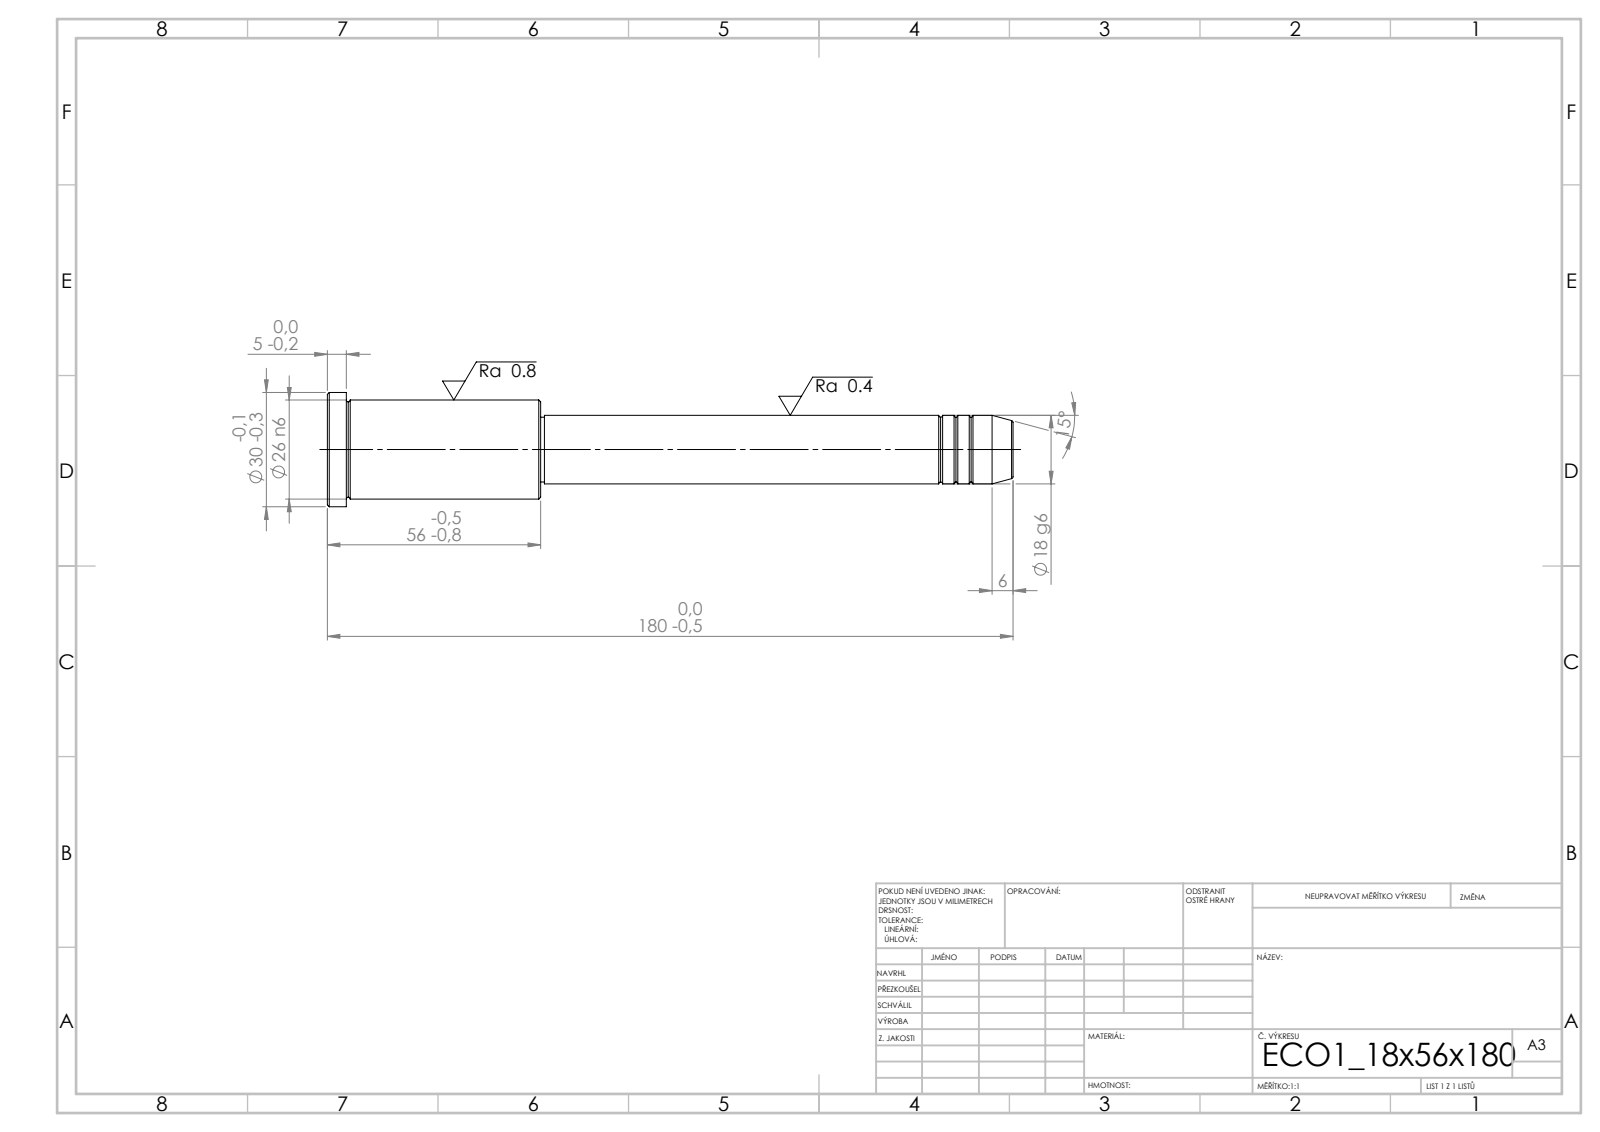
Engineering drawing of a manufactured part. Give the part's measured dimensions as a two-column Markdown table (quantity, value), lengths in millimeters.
| quantity | value |
| --- | --- |
| STEP written by | SolidWorks 2019 (CONFIG_CONTROL_DESIGN) |
| units | millimeters |
| bodies | 1 solid, 43 faces (5 planar, 14 cylindrical, 24 other) |
| overall size | 180 × 30 × 30 |
| volume | 61 802 mm³ |
| surface area | 13 096 mm² |
| round bosses / shafts (diameter × count) | 30 × 1, 26 × 1, 18 × 1, 17 × 1 |
| main face-to-face distances | 56, 51, 5, 124, 175, 180, 123, 1, 52, 57 |
